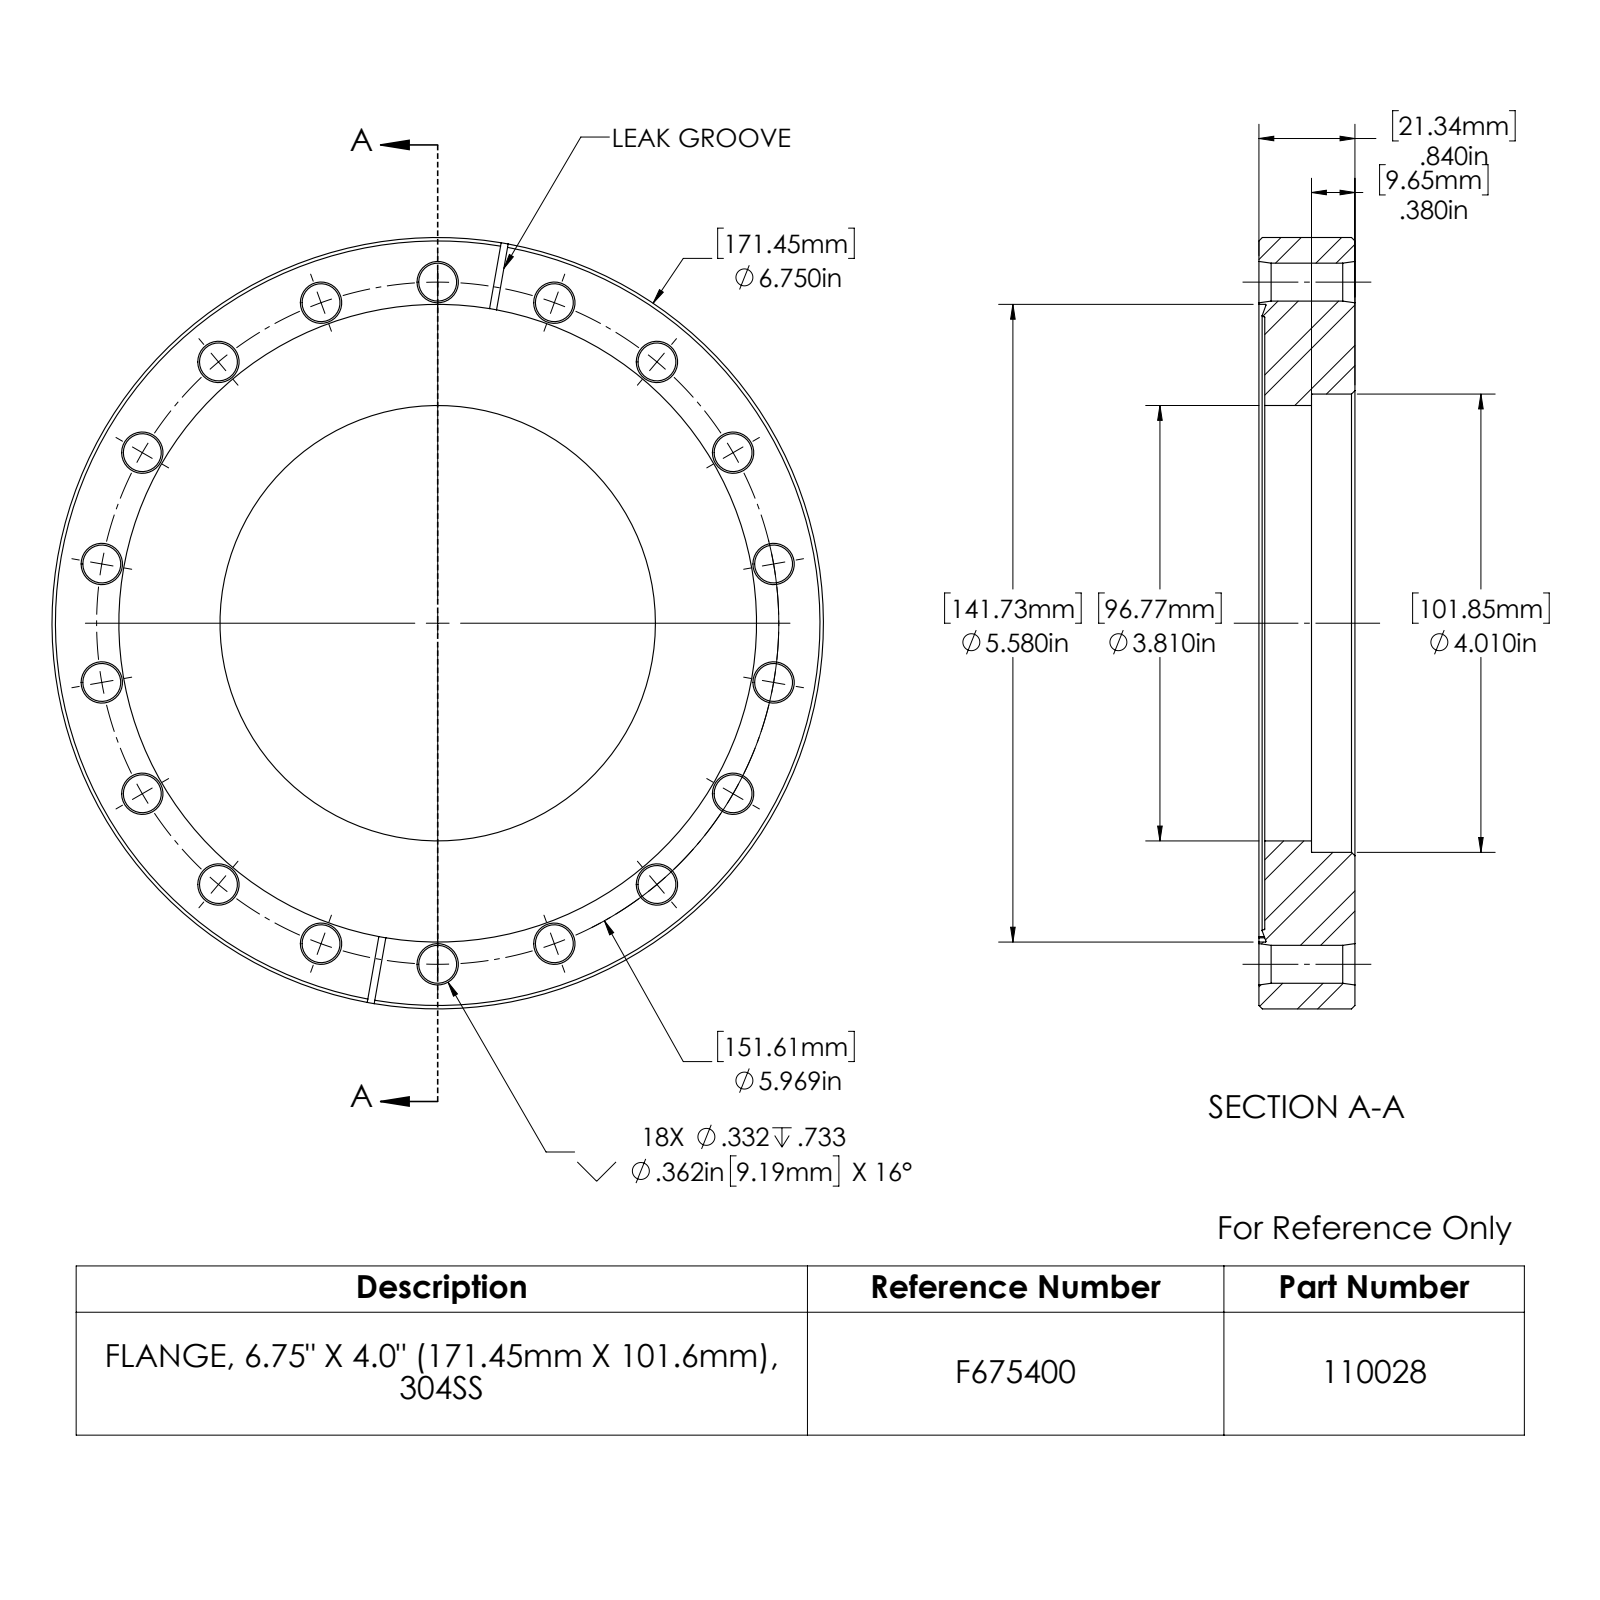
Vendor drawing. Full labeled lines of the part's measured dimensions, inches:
Part name (STEP PRODUCT): 110028
STEP written by: SolidWorks 2022 (AUTOMOTIVE_DESIGN)
Units: inches
Bodies: 1 solid, 146 faces (11 planar, 44 cylindrical, 91 other)
Overall size (bounding box): 6.75 × 6.75 × 0.84
Volume: 17.99 in³ · Surface area: 89.1 in²
Round holes (diameter × count): ⌀0.332 ×18, ⌀3.81 ×1, ⌀4.01 ×1, ⌀5.58 ×1
Round bosses / shafts (diameter × count): ⌀6.75 ×1
Main face-to-face distances: 0.789, 0.051, 0.84, 0.46, 0.409, 0.38, 0.052, 0.408, 0.788, 0.062
Hole centre spacings: 2.984, 1.037, 2.985, 4.572, 2.041, 5.878, 3.837, 5.169
